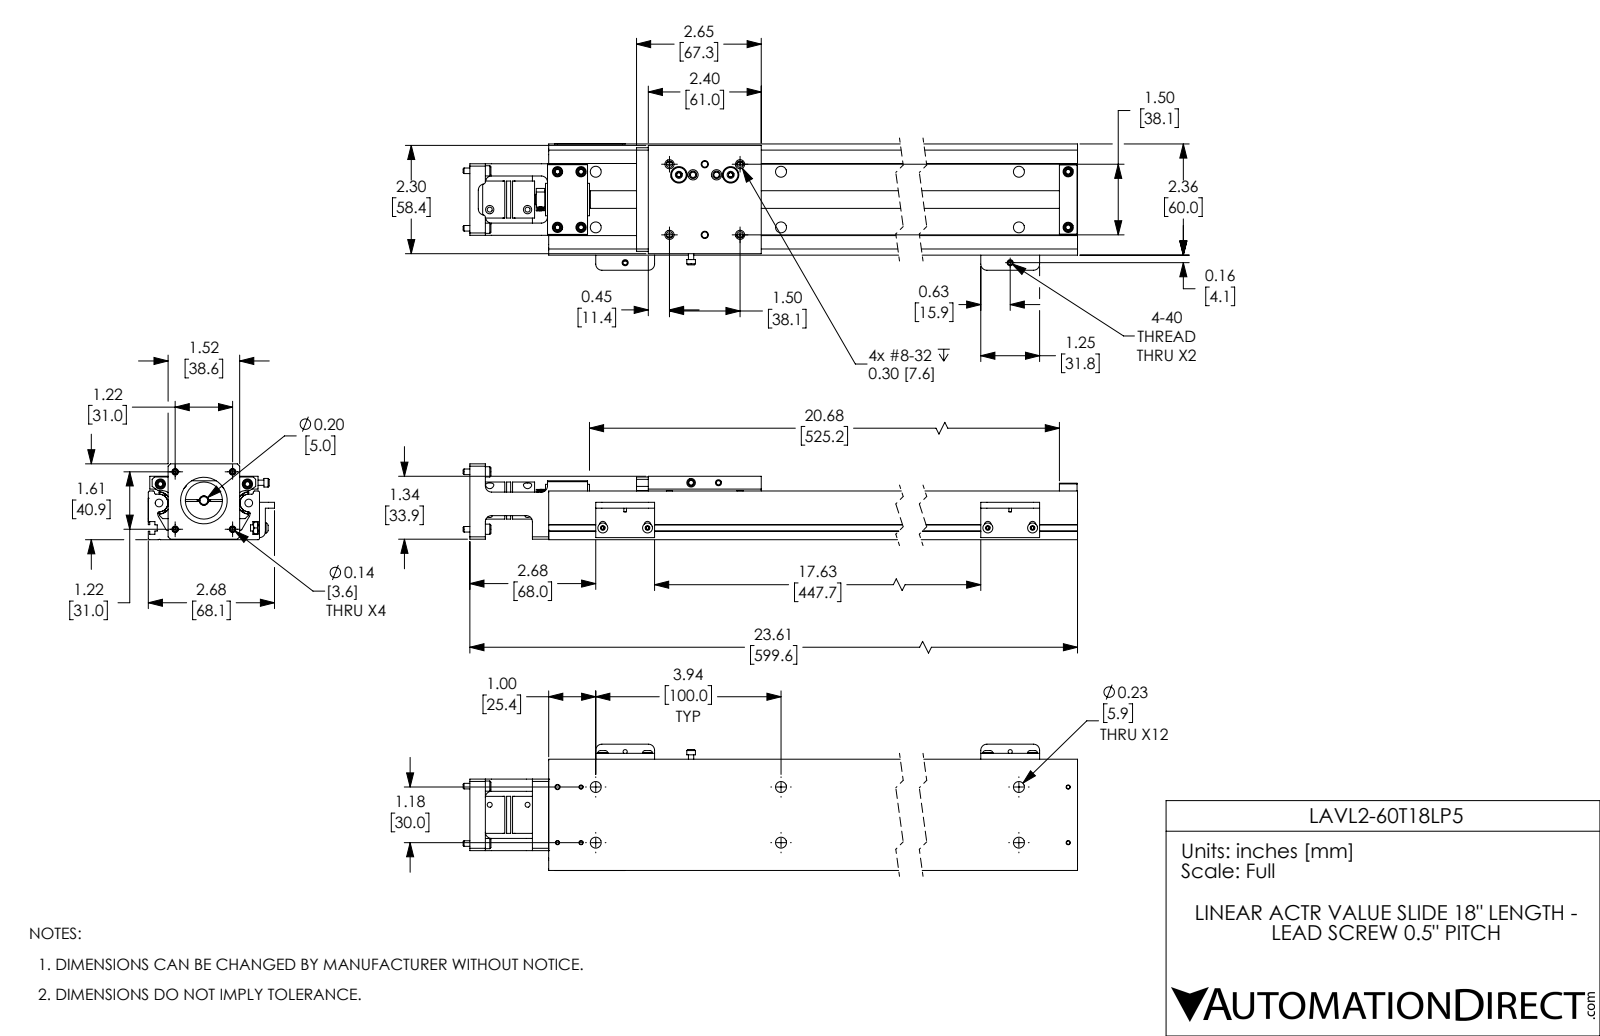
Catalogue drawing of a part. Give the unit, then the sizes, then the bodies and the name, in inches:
Units: inches
Overall size (bounding box): 23.748 × 2.683 × 1.612
Round holes (diameter × count): ⌀0.089 ×18, ⌀0.234 ×12, ⌀0.141 ×10, ⌀0.219 ×10, ⌀0.136 ×6, ⌀0.141 ×4, ⌀0.03 ×2, ⌀0.1 ×2, ⌀0.106 ×2, ⌀0.125 ×2, ⌀0.159 ×2, ⌀0.165 ×2
Round bosses / shafts (diameter × count): ⌀0.112 ×15, ⌀0.183 ×11, ⌀0.217 ×4, ⌀0.213 ×4, ⌀0.118 ×4, ⌀0.312 ×2, ⌀0.19 ×2, ⌀0.164 ×2
Partial cylindrical surfaces — rounded edges, fillets, slot ends (radius × count): R0.13 ×20, R0.03 ×12, R0.07 ×8, R0.06 ×4, R0.02 ×3, R0.04 ×2, R0.05 ×2, R0.065 ×2
Main face-to-face distances: 0.2, 2.362, 0.14, 0.115, 0.185, 2.222, 0.11, 0.03, 2.332, 2.192
Hole centre spacings: 3.937, 4.11, 1.181, 7.874, 7.962, 11.811, 11.87, 0.863
Volume: 27.93 in³ · Surface area: 369.6 in²
Bodies: 52 solids, 2136 faces (1295 planar, 533 cylindrical, 308 other)
Part name (STEP PRODUCT): LAVL2-60T18LP5; LAVL2-60T18LP5_BLOCK; LAVL2-60T18LP5_BODY
STEP written by: SolidWorks 2017 (AUTOMOTIVE_DESIGN)
